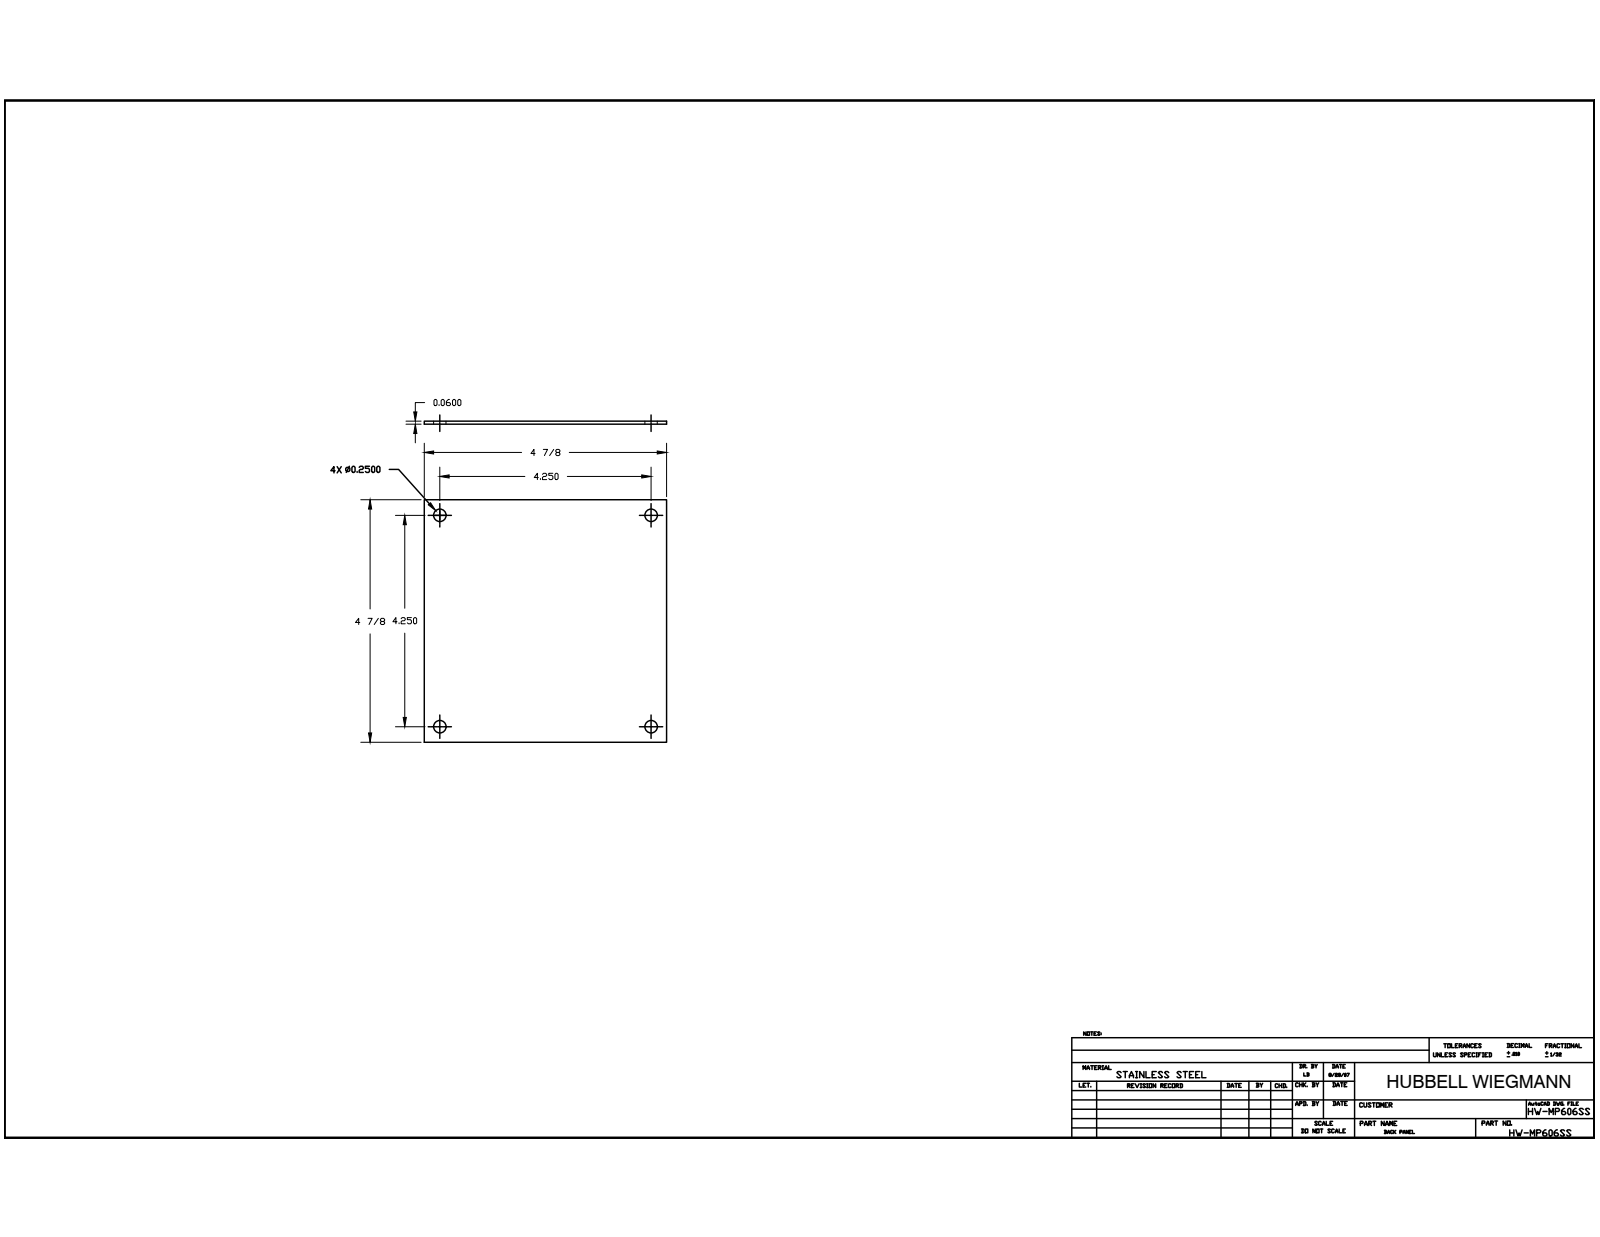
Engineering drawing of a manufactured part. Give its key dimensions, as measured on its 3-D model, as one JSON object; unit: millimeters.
{"part_name": "BP66SS_STP", "step_written_by": "Autodesk Inventor 2014 (AUTOMOTIVE_DESIGN)", "units": "millimeters", "bodies": {"solids": 1, "faces": 10, "planar": 6, "cylindrical": 4, "other": 0}, "overall_size": [123.83, 123.83, 1.52], "volume_mm3": 23174, "surface_area_mm2": 31288, "round_holes": [[6.35, 4]], "face_to_face_distances": [1.52, 123.82], "hole_center_spacings": [107.94, 152.65]}
